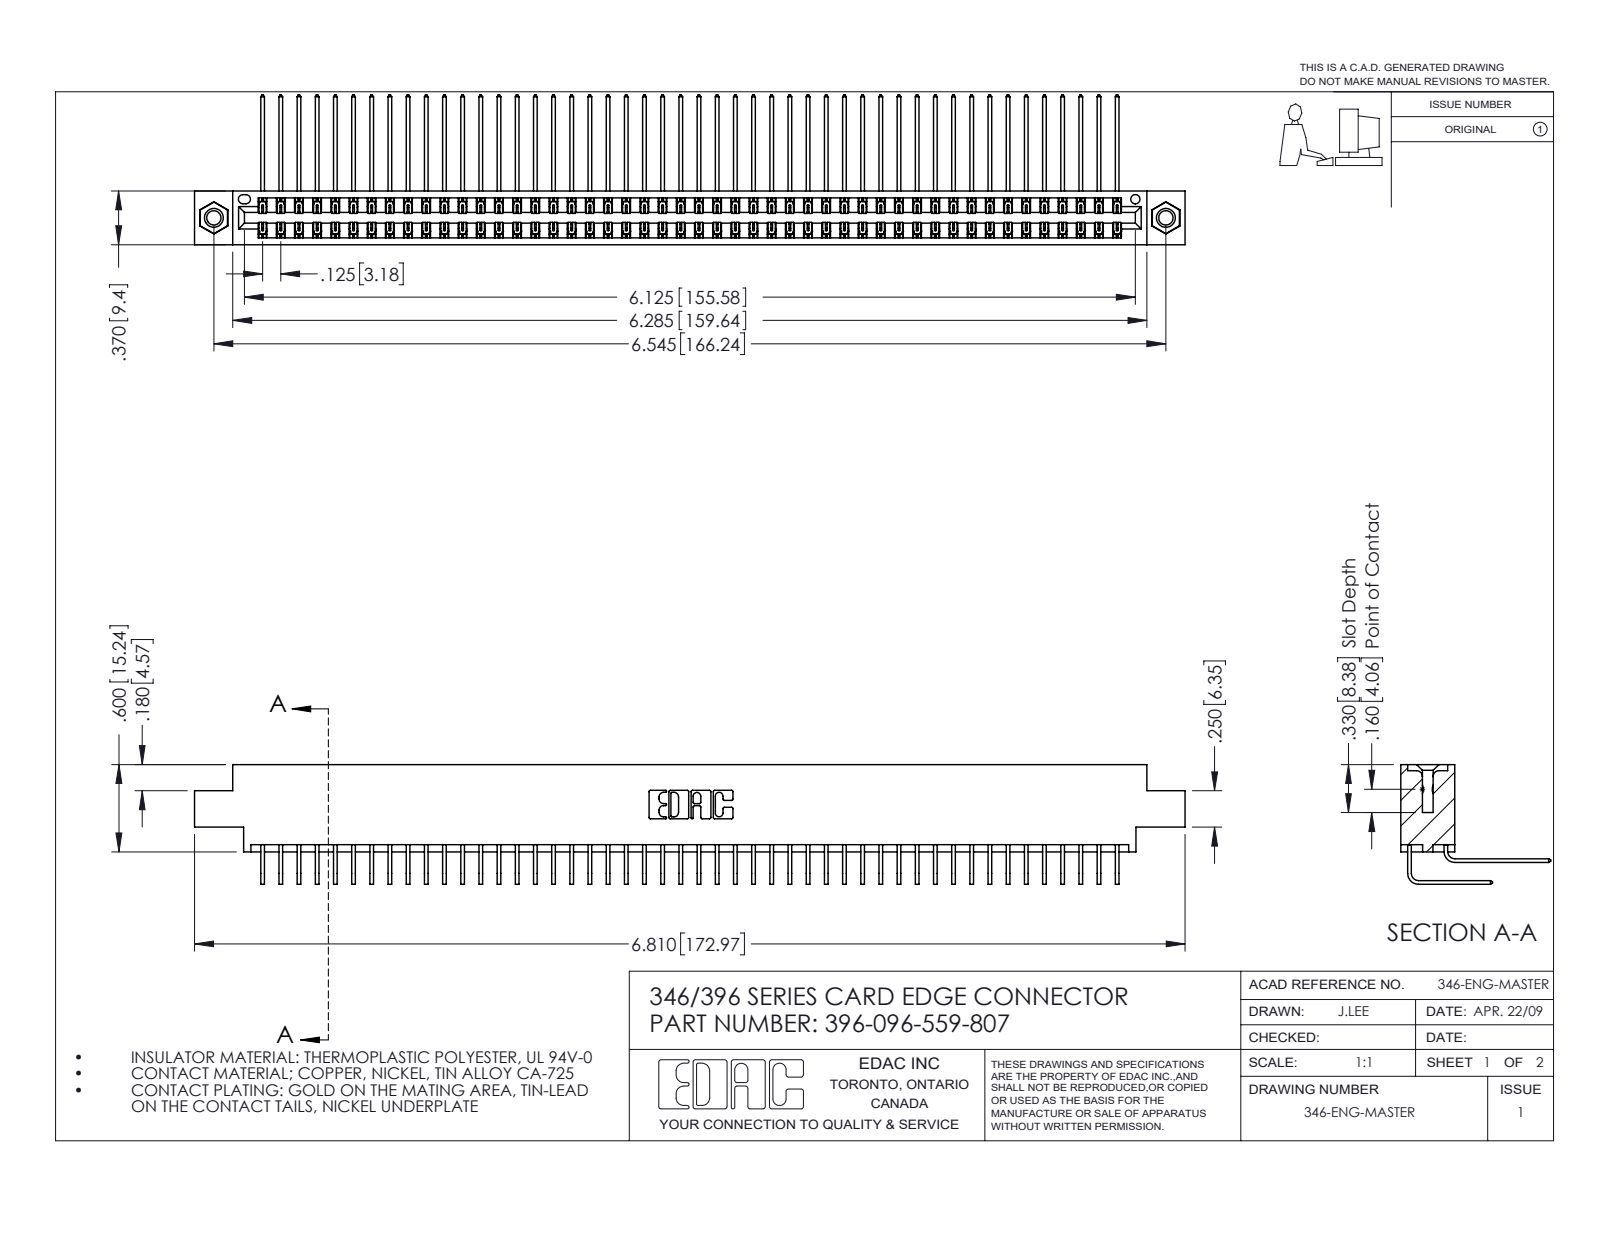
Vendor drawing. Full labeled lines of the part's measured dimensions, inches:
Part name (STEP PRODUCT): 345-250-001_345-250-005-103; 346 Part_0.170 Offset - 0.156 Dia-TI; 345-292-001_558 559 Tail - 1; 396-096-559-807 (+1 more)
STEP written by: SolidWorks 2016 (CONFIG_CONTROL_DESIGN)
Units: inches
Bodies: 99 solids, 5370 faces (3664 planar, 1690 cylindrical, 16 other)
Overall size (bounding box): 6.81 × 1.03 × 0.823
Volume: 1.056 in³ · Surface area: 41.45 in²
Round holes (diameter × count): ⌀0.098 ×2, ⌀0.125 ×2, ⌀0.156 ×2, ⌀0.064 ×1
Round bosses / shafts (diameter × count): ⌀0.155 ×2
Partial cylindrical surfaces — rounded edges, fillets, slot ends (radius × count): R0.006 ×144, R0.01 ×22, R0.007 ×6, R0.031 ×6, R0.026 ×3, R0.014 ×2, R0.022 ×2, R0.024 ×2
Main face-to-face distances: 0.048, 0.322, 0.025, 0.37, 0.25, 0.072, 0.298, 0.275, 0.222, 0.148
Hole centre spacings: 0.246, 6.336, 6.545
